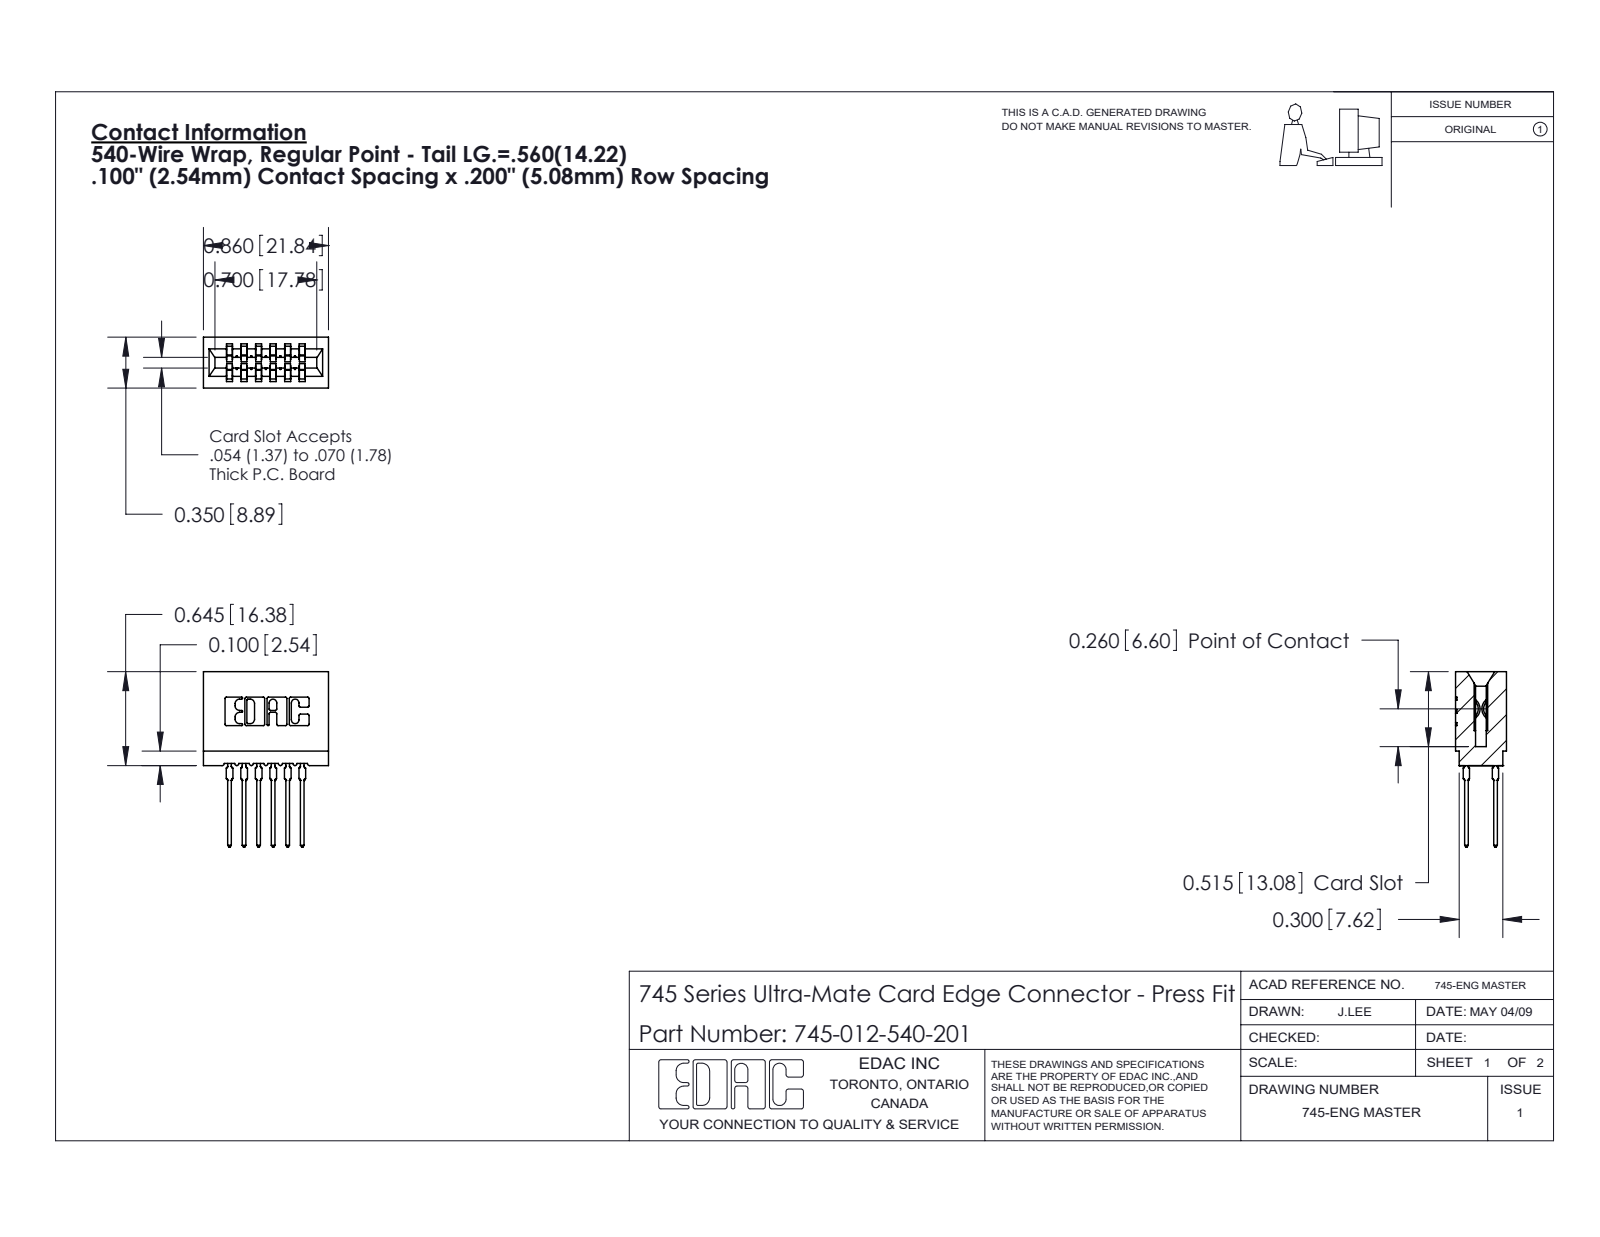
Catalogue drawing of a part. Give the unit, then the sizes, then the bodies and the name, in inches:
Units: inches
Overall size (bounding box): 1.206 × 0.86 × 0.35
Partial cylindrical surfaces — rounded edges, fillets, slot ends (radius × count): R0.021 ×24, R0.01 ×22, R0.015 ×12, R0.005 ×8, R0.011 ×8, R0.007 ×6, R0.031 ×6, R0.026 ×3
Main face-to-face distances: 0.1, 0.2, 0.042, 0.3, 0.142, 0.058, 0.242, 0.4, 0.158, 0.35
Volume: 0.136 in³ · Surface area: 5.919 in²
Bodies: 13 solids, 1169 faces (607 planar, 250 cylindrical, 312 other)
Part name (STEP PRODUCT): 745-292-001_540; 745-012-540-201; 745 Part_Insulator Option - 01
STEP written by: SolidWorks 2020 (CONFIG_CONTROL_DESIGN)
